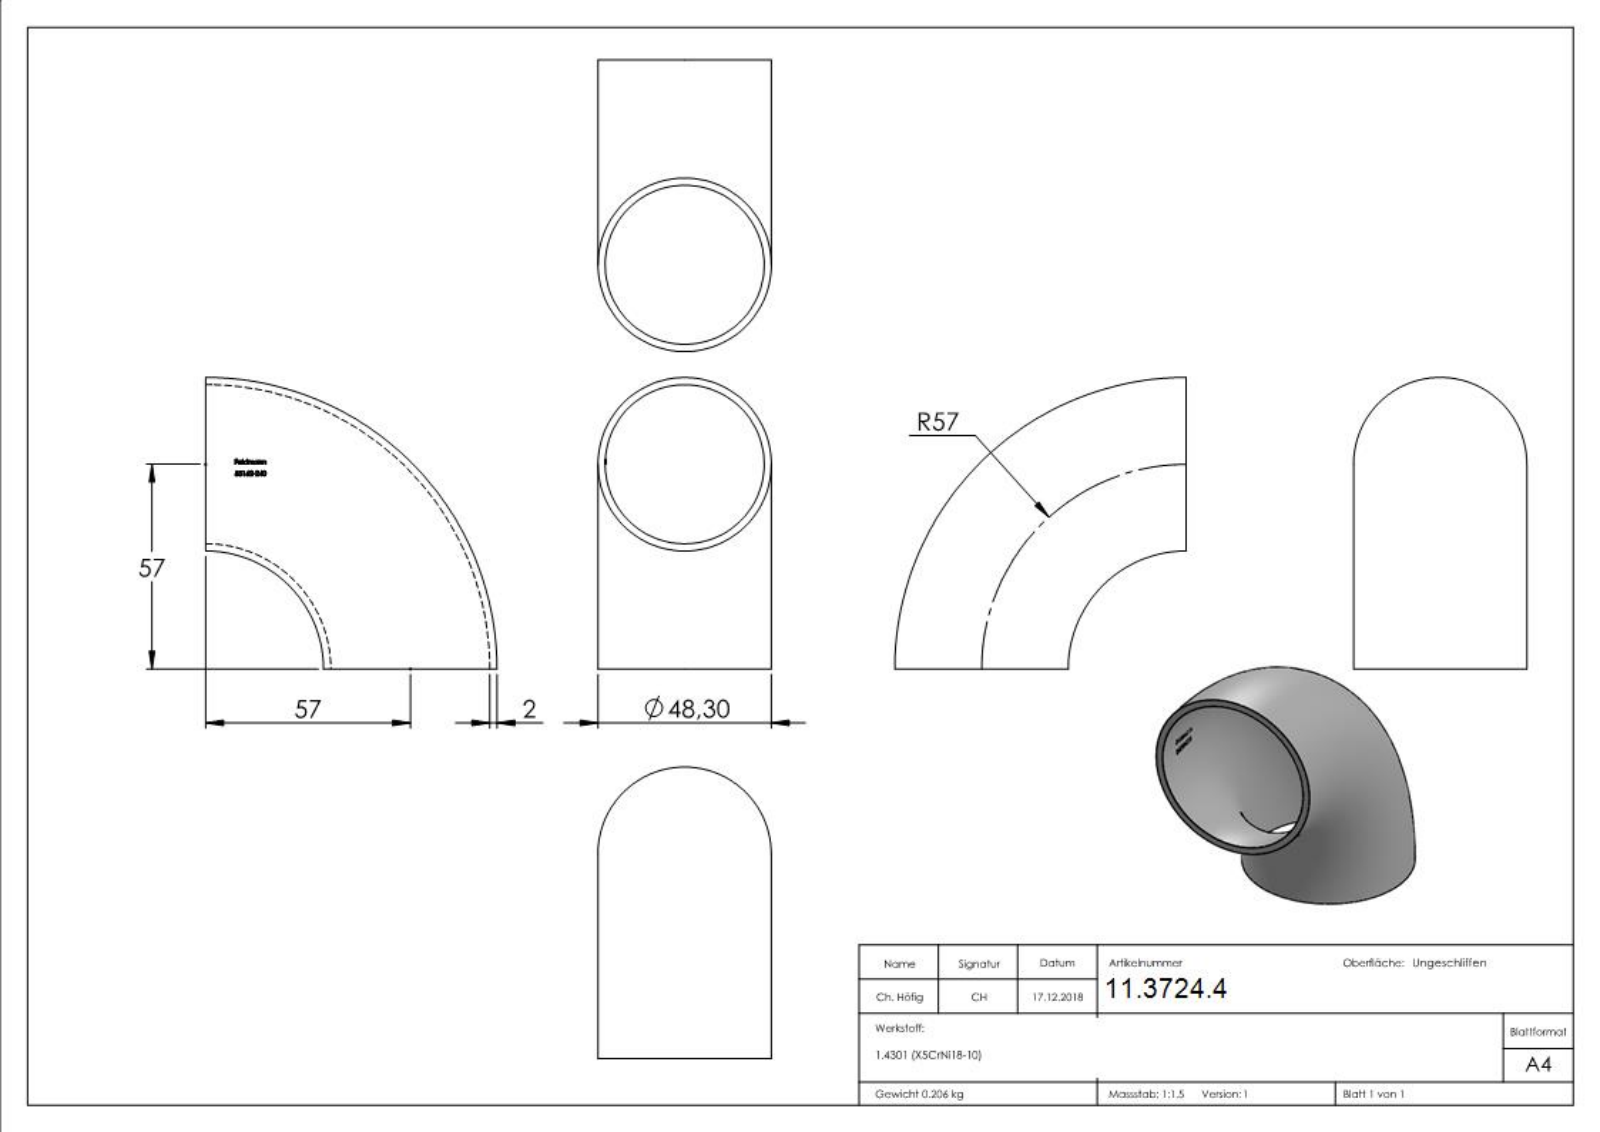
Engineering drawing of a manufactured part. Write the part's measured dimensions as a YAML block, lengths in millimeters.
part_name: "55162-240"
step_written_by: "SolidWorks 2015 (CONFIG_CONTROL_DESIGN)"
units: millimeters
bodies: {solids: 1, faces: 227, planar: 106, cylindrical: 0, other: 121}
overall_size: [81.15, 81.15, 48.3]
volume: 26046
surface_area: 26638
face_to_face_distances: [0.39, 1.26, 1.32, 1.19, 2.97, 4.23, 2.02, 3.66, 3.27, 2.4]
